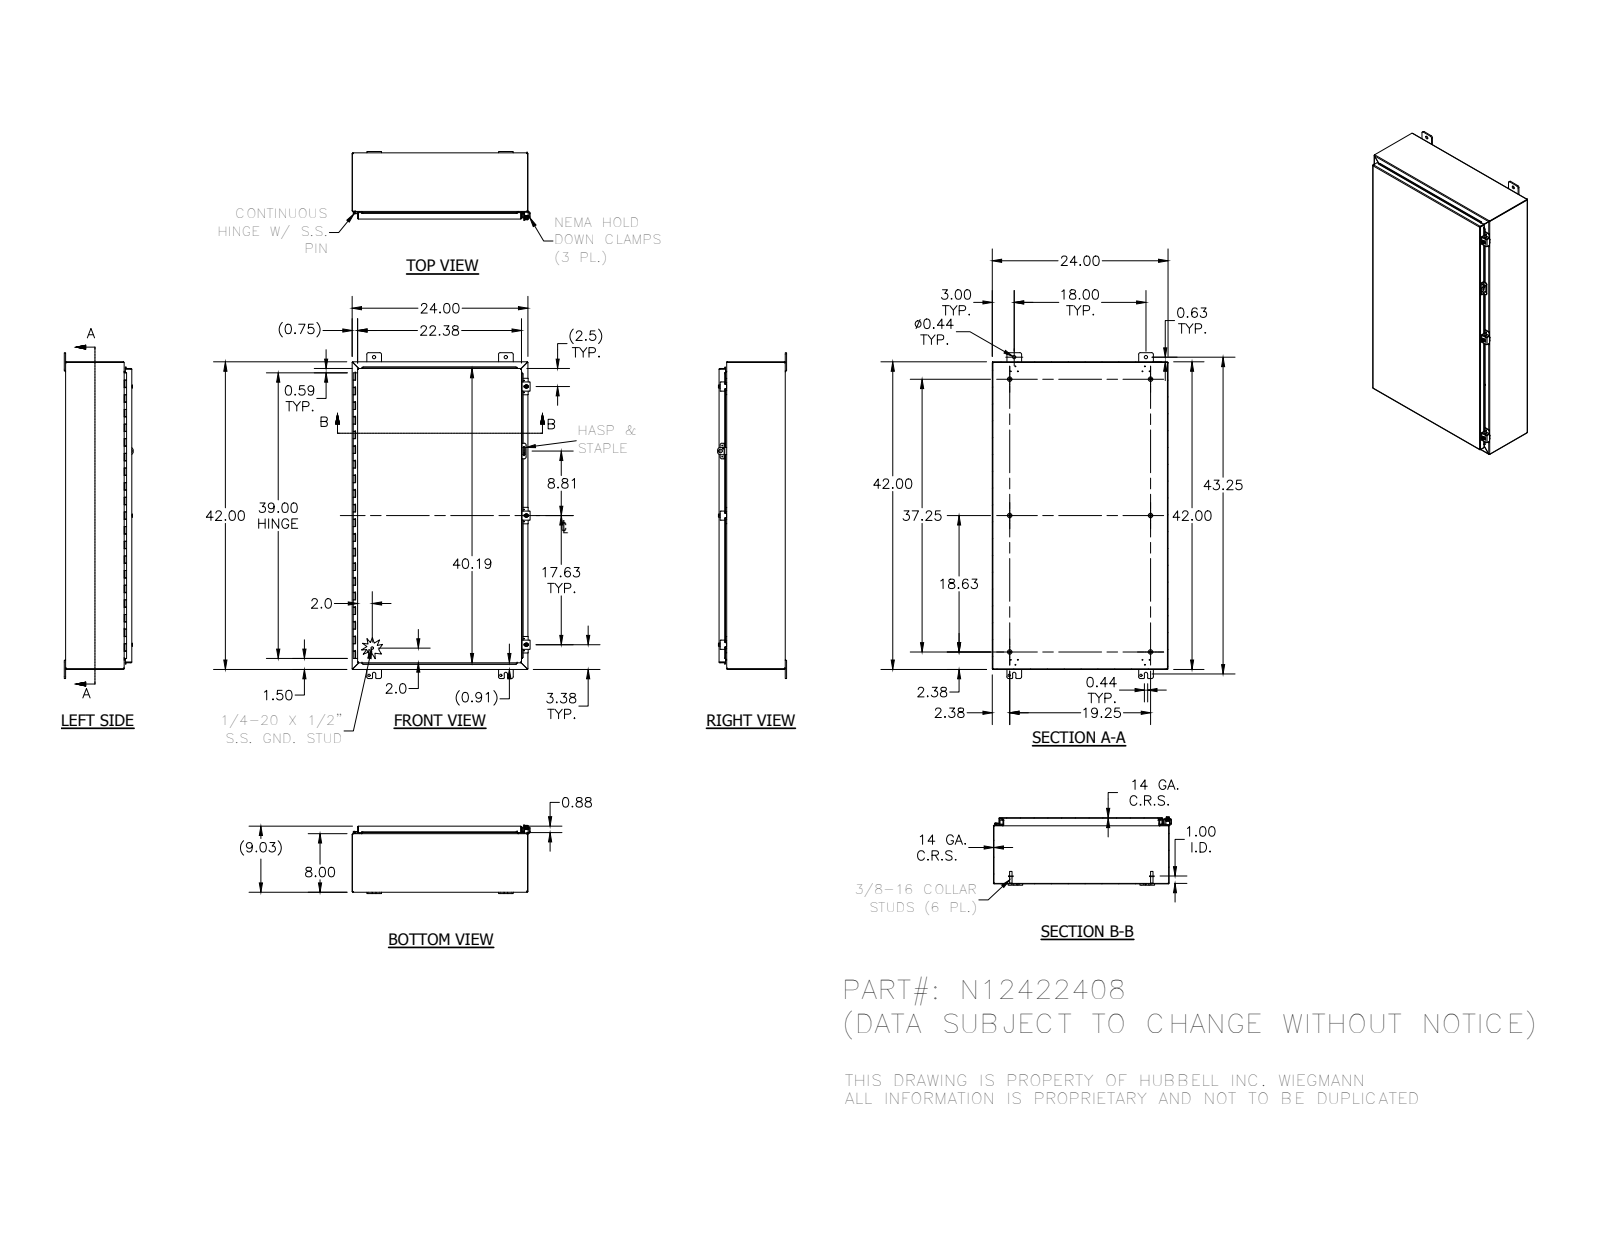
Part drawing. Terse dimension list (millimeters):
name: N12422408; 34840; 38420; N12422408BKP (+8 more)
written by: Autodesk Inventor 2012 (AUTOMOTIVE_DESIGN)
unit: mm
bodies: 34 solids, 1288 faces (707 planar, 438 cylindrical, 143 other)
size: 1130.3 × 617.5 × 239
volume: 4 457 000 mm³; area: 4 617 000 mm²
holes: 12× ⌀3, 9× ⌀2.8, 4× ⌀8, 4× ⌀11.1, 3× ⌀5.4, 3× ⌀7.1, 3× ⌀7.6, 1× ⌀3.2, 1× ⌀4, 1× ⌀12.7
bosses: 6× ⌀15.9, 6× ⌀8.4, 5× ⌀6.4, 3× ⌀13.2, 3× ⌀12.7, 3× ⌀8.9, 2× ⌀2.9, 1× ⌀8.6
rounds: 39× R0.8, 31× R1.6, 27× R3.2, 27× R6.4, 23× R0.8, 23× R2.7, 8× R1.8, 6× R2.5
face distances: 1.9, 227.6, 225.7, 229.4, 607.7, 1064.9, 201.3, 26.2, 605.8, 609.6
hole spacings: 457.2, 19.3, 21.3, 22.3, 23.9, 24.6, 50.7, 441.2
